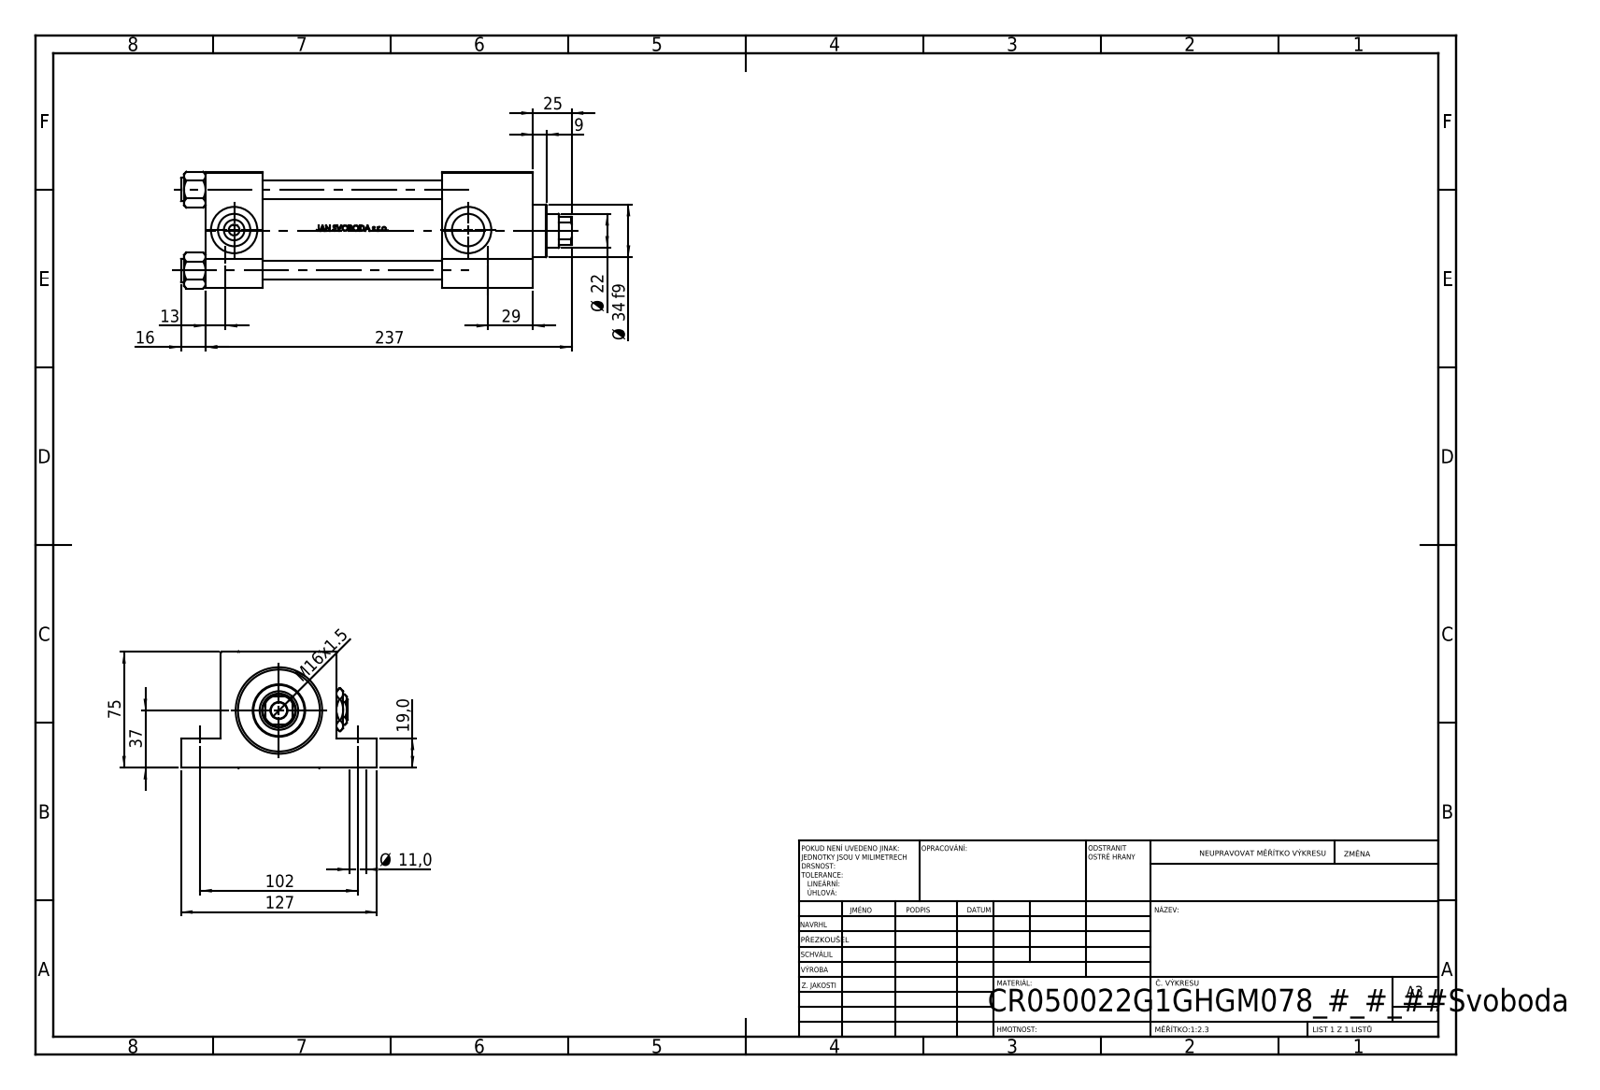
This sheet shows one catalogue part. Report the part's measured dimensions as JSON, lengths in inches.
{"part_name": "V215CR_G_TYCINKA; Zatka_pro_OIL_PORT; NUT_M5_G; V215CR_G_Body (+2 more)", "step_written_by": "SolidWorks 2019 (CONFIG_CONTROL_DESIGN)", "units": "inches", "bodies": {"solids": 12, "faces": 1134, "planar": 454, "cylindrical": 128, "other": 552}, "overall_size": [9.961, 5, 2.974], "volume_in3": 50.63, "surface_area_in2": 299.7, "round_holes": [[0.433, 4], [0.472, 4], [0.276, 2], [0.825, 2], [1.181, 2], [0.413, 1], [0.866, 1], [0.984, 1], [1.614, 1], [1.969, 1], [2.087, 1]], "round_bosses_or_shafts": [[0.591, 4], [2.205, 1], [1.339, 1]], "partial_cylinders_radius": [[0.413, 1]], "face_to_face_distances": [2.953, 1.457, 8.346, 6.89, 0.748, 2.205, 6.024, 4.567, 2.323, 1.024], "hole_center_spacings": [2.059, 1.442, 1.47, 2.912, 4.016, 6.693, 7.805, 5.965]}
